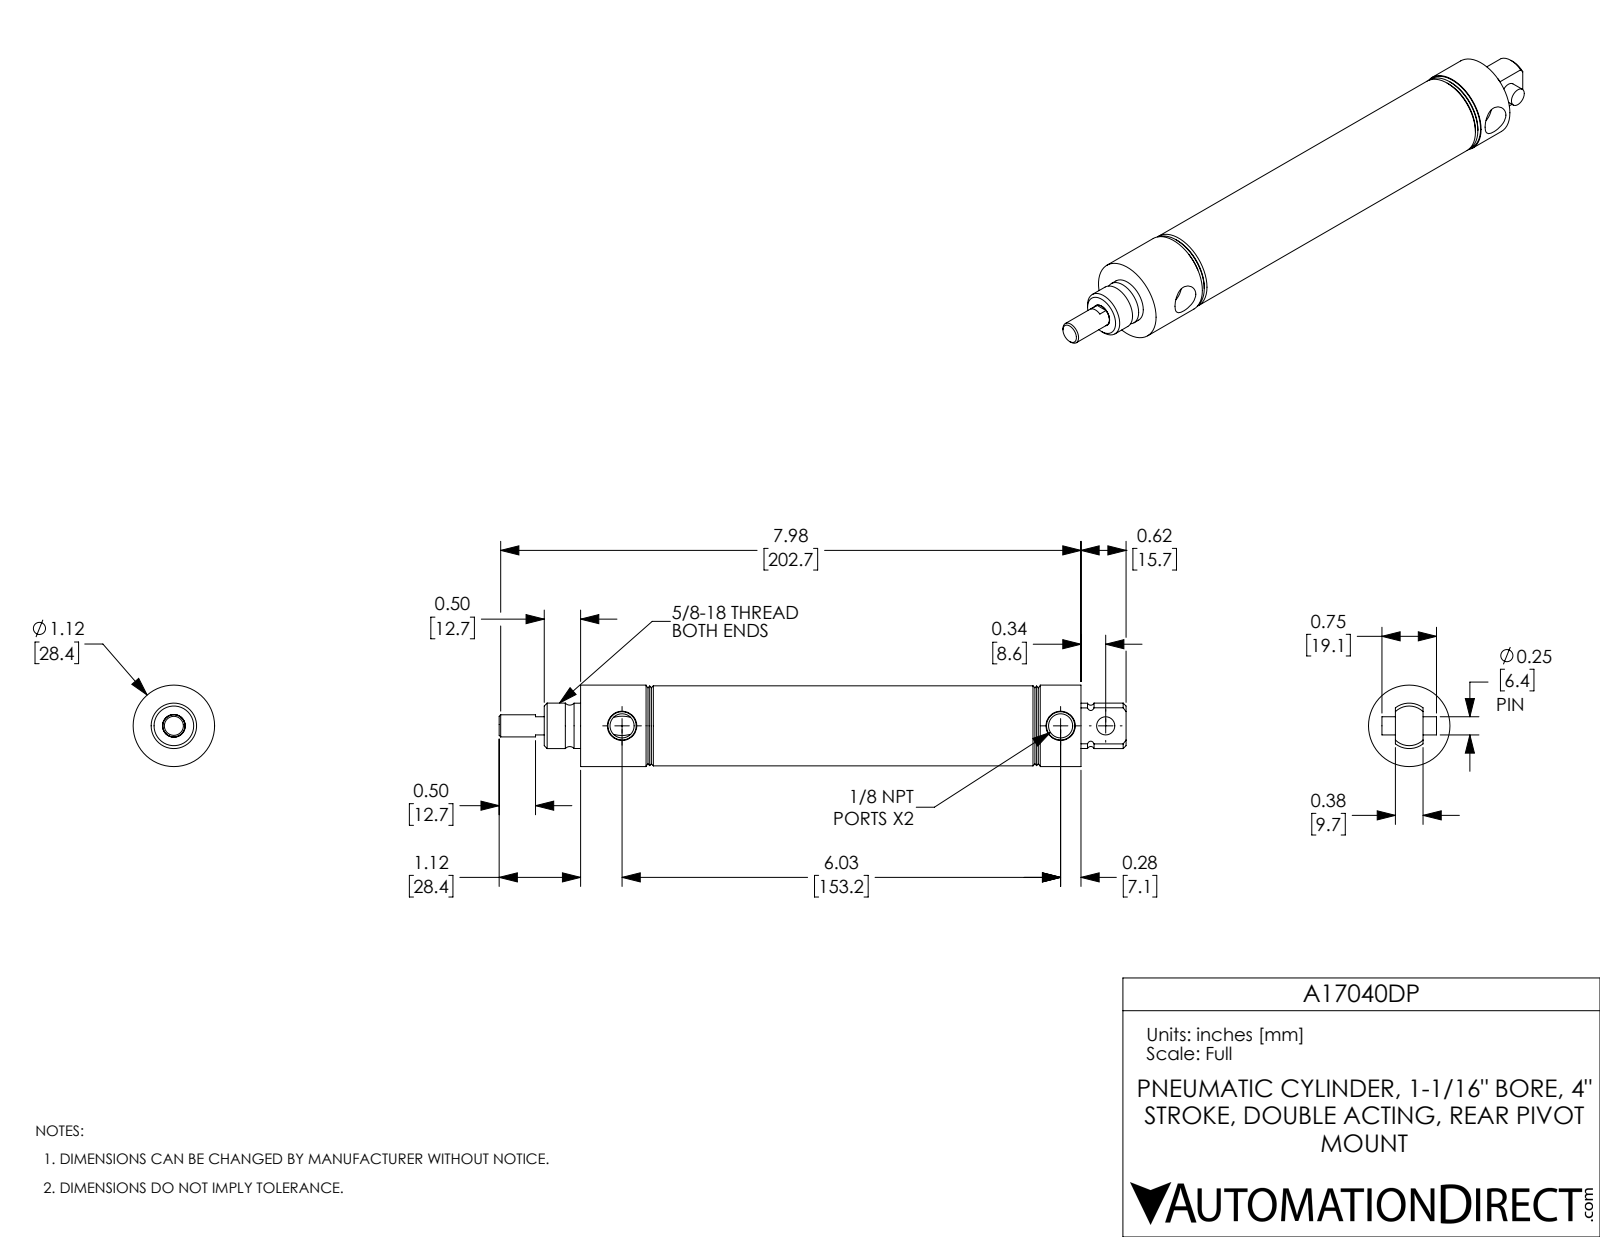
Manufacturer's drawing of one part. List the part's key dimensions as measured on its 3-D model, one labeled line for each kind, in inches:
Part name (STEP PRODUCT): A17040DP-MainBody; A17040DP; A17040DP-PIN; A17040DP-Rod
STEP written by: SolidWorks 2017 (AUTOMOTIVE_DESIGN)
Units: inches
Bodies: 3 solids, 92 faces (22 planar, 32 cylindrical, 38 other)
Overall size (bounding box): 8.62 × 1.12 × 1.12
Volume: 3.586 in³ · Surface area: 57.85 in²
Round holes (diameter × count): ⌀0.332 ×2, ⌀0.25 ×1, ⌀0.312 ×1, ⌀1.063 ×1
Round bosses / shafts (diameter × count): ⌀1.12 ×1, ⌀1.1 ×1, ⌀0.625 ×1, ⌀0.623 ×1, ⌀0.304 ×1
Partial cylindrical surfaces — rounded edges, fillets, slot ends (radius × count): R0.313 ×1
Main face-to-face distances: 0.5, 5.69, 4.5, 4, 1.19, 1.69, 5.69, 6.88, 5.19, 1.19
Hole centre spacings: 0.62, 6.03, 6.65
